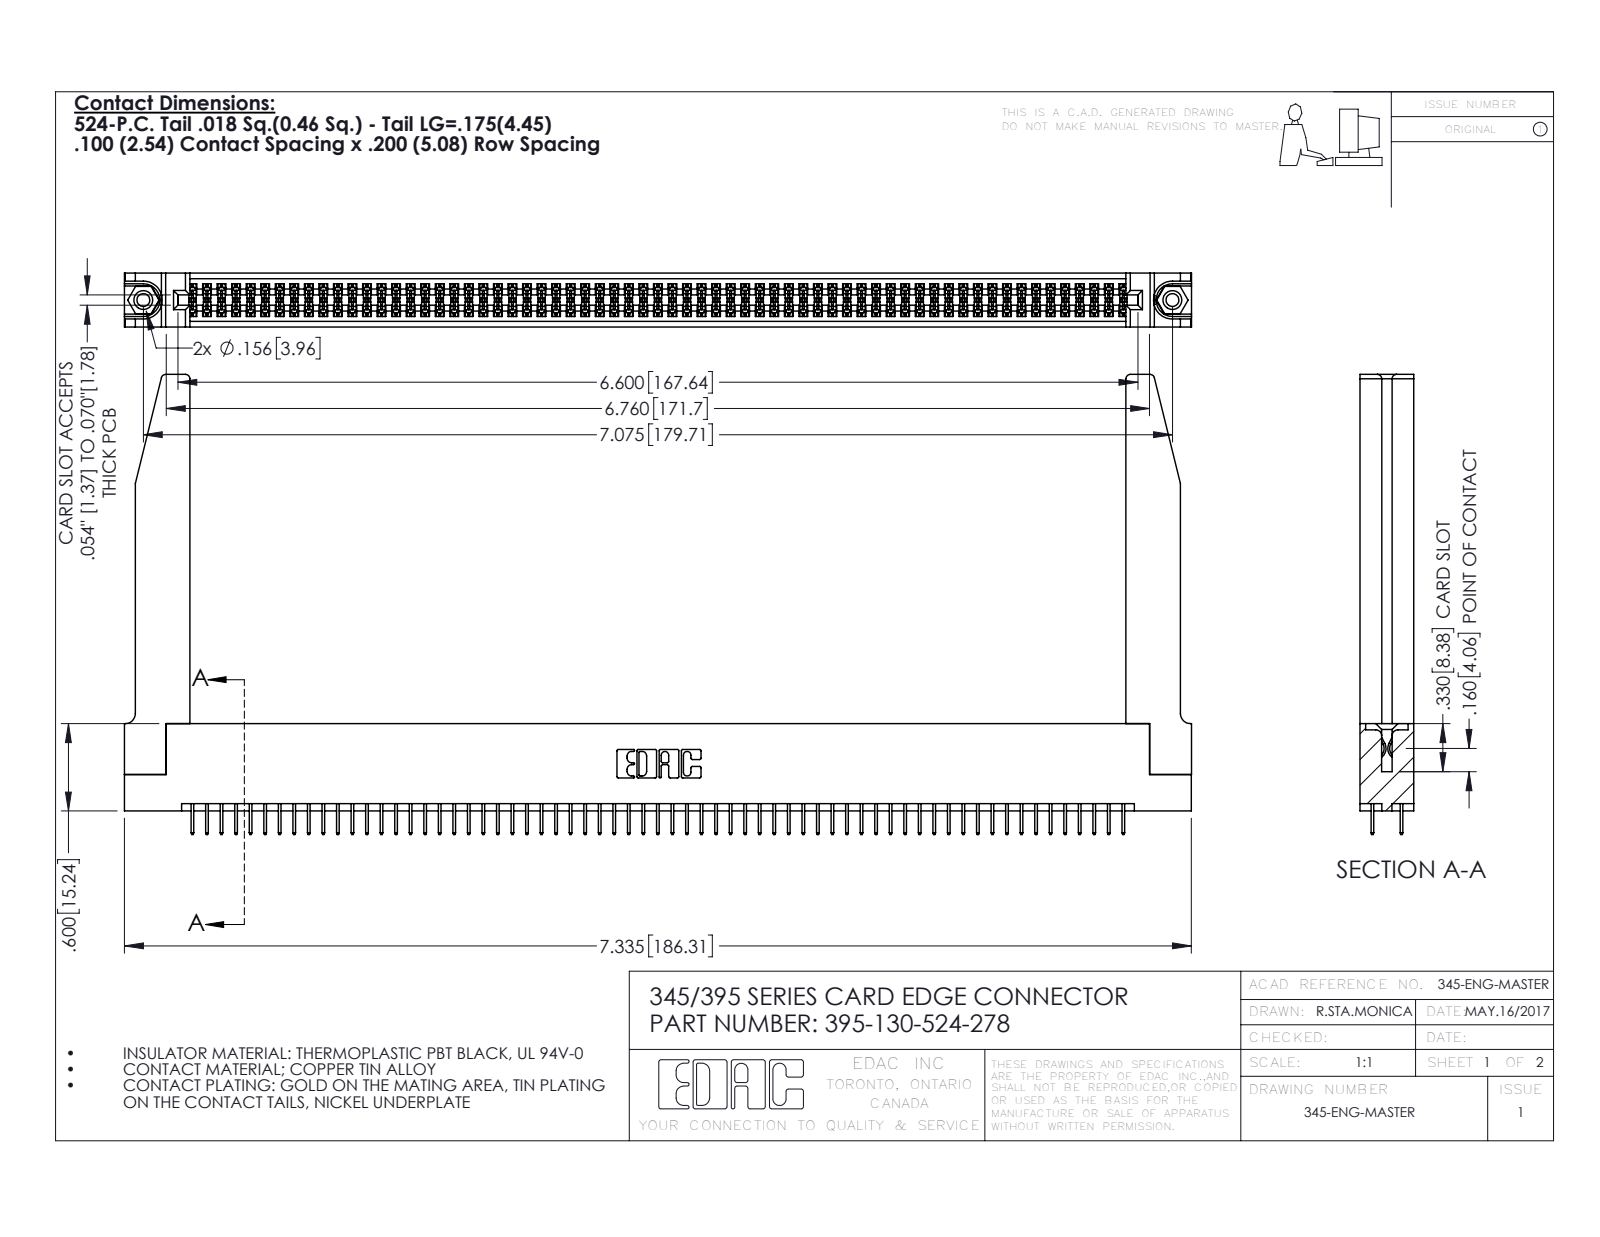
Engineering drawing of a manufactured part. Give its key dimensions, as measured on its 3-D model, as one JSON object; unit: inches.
{"part_name": "345-250-001_345-250-001-102; 345 Part_Flush Mounting Lugs - 0.156 Dia-TH; 395-130-524-278; 345-220-078_345-220-078 (+1 more)", "step_written_by": "SolidWorks 2016 (CONFIG_CONTROL_DESIGN)", "units": "inches", "bodies": {"solids": 135, "faces": 7380, "planar": 5292, "cylindrical": 2036, "other": 52}, "overall_size": [7.336, 3.162, 0.37], "volume_in3": 1.58, "surface_area_in2": 52, "round_holes": [[0.089, 2], [0.125, 2], [0.156, 2], [0.064, 1]], "round_bosses_or_shafts": [[0.155, 2]], "partial_cylinders_radius": [[0.006, 195], [0.01, 22], [0.03, 8], [0.007, 6], [0.031, 6], [0.026, 3], [0.014, 2], [0.019, 2]], "face_to_face_distances": [0.072, 0.37, 0.298, 0.2, 0.098, 0.272, 0.025, 0.225, 0.072, 0.175], "hole_center_spacings": [0.27, 6.839, 7.075]}
